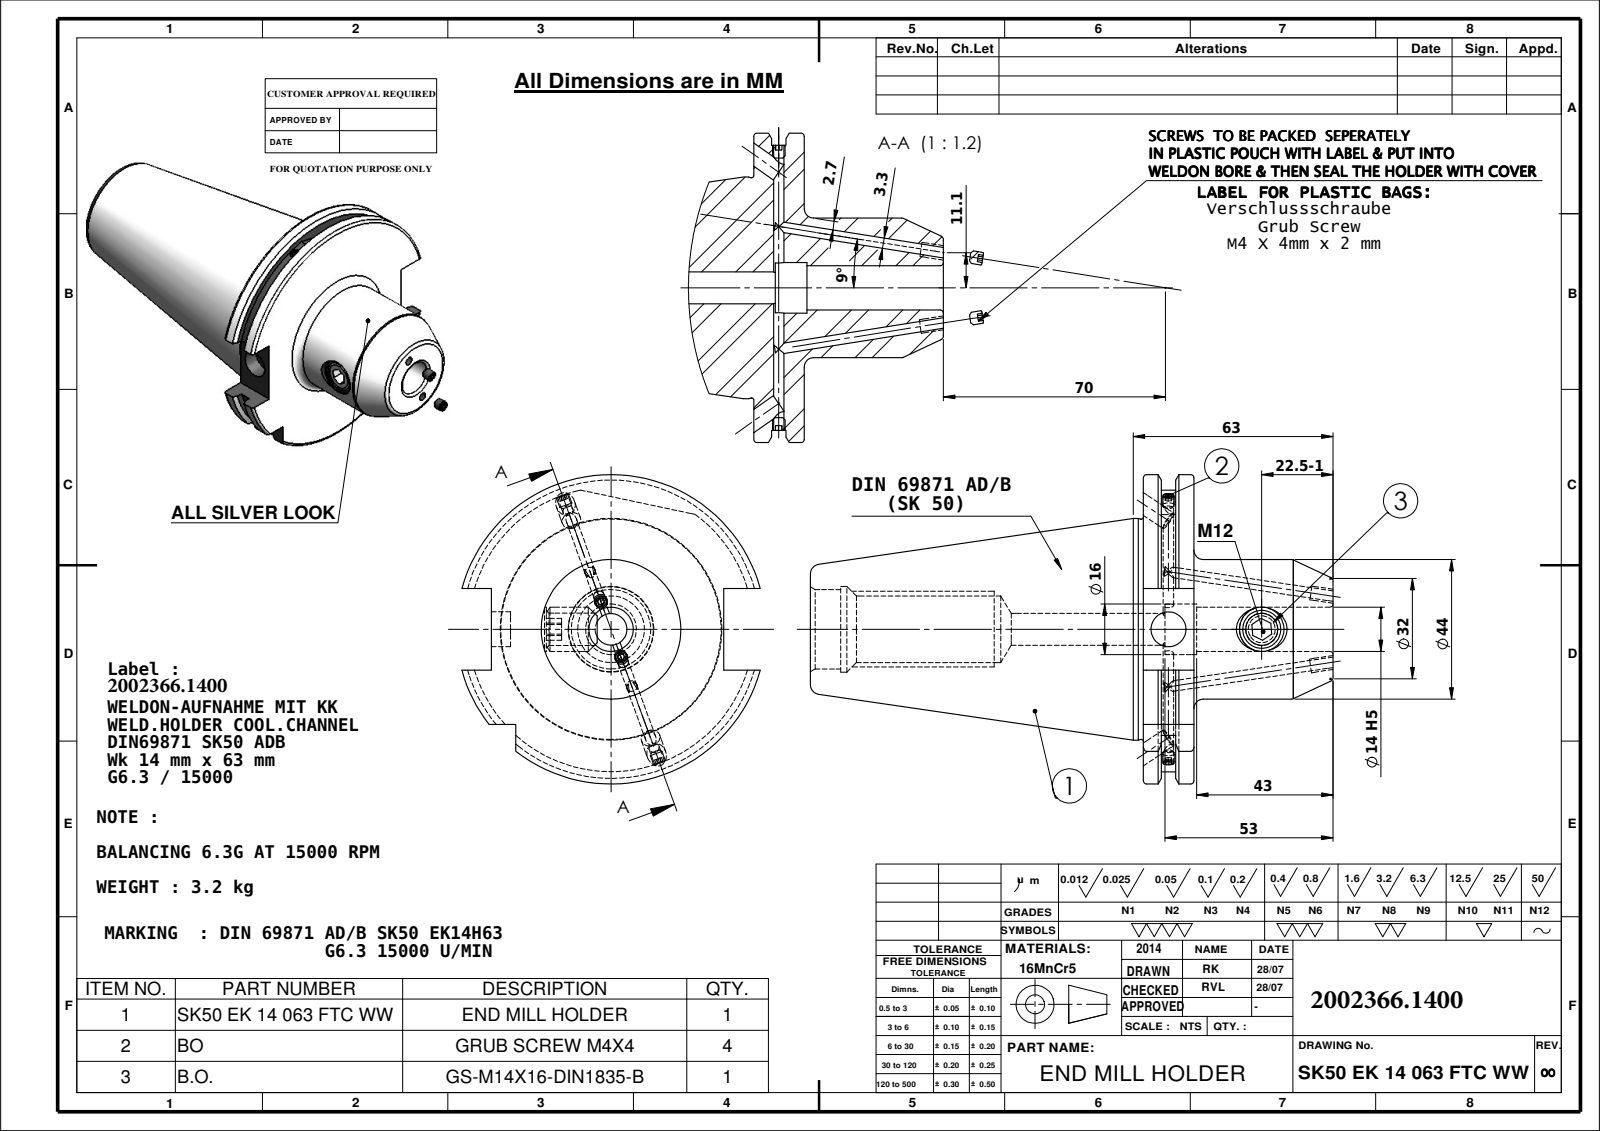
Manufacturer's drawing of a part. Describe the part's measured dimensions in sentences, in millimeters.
The part is named "SK50 EK 14 063 FTC WW; Copy of M4X4_DIN 913 - M4 x 4-N; M14X16_ISO 4026 - M12 x 12-N". Its 3-D file was written by "SolidWorks 2009 (CONFIG_CONTROL_DESIGN)". It is 6 solids with 211 faces: 76 planar, 69 cylindrical and 66 other. Overall it measures 177.35 by 97.5 by 94.05 millimeters. Its volume is 387 837 cubic millimeters and its surface area 53 157 square millimeters. Round holes: 3 of diameter 3.3, 2 of diameter 6, 2 of diameter 14, 1 of diameter 10, 1 of diameter 10.2, 1 of diameter 11, 1 of diameter 16, 1 of diameter 21, 1 of diameter 25, 1 of diameter 27. Round bosses or shafts: 4 of diameter 4, 1 of diameter 69.85, 1 of diameter 69.45, 1 of diameter 44. Partial cylindrical surfaces (rounded edges, fillets, slot ends): 1 of radius 44.9, 1 of radius 48.75. The main face-to-face distances are 15.9, 10.15, 5.75, 5.66, 4.49, 10.24, 59.8, 54.14, 49.65, 43.9. The hole center spacings are 29.4.
